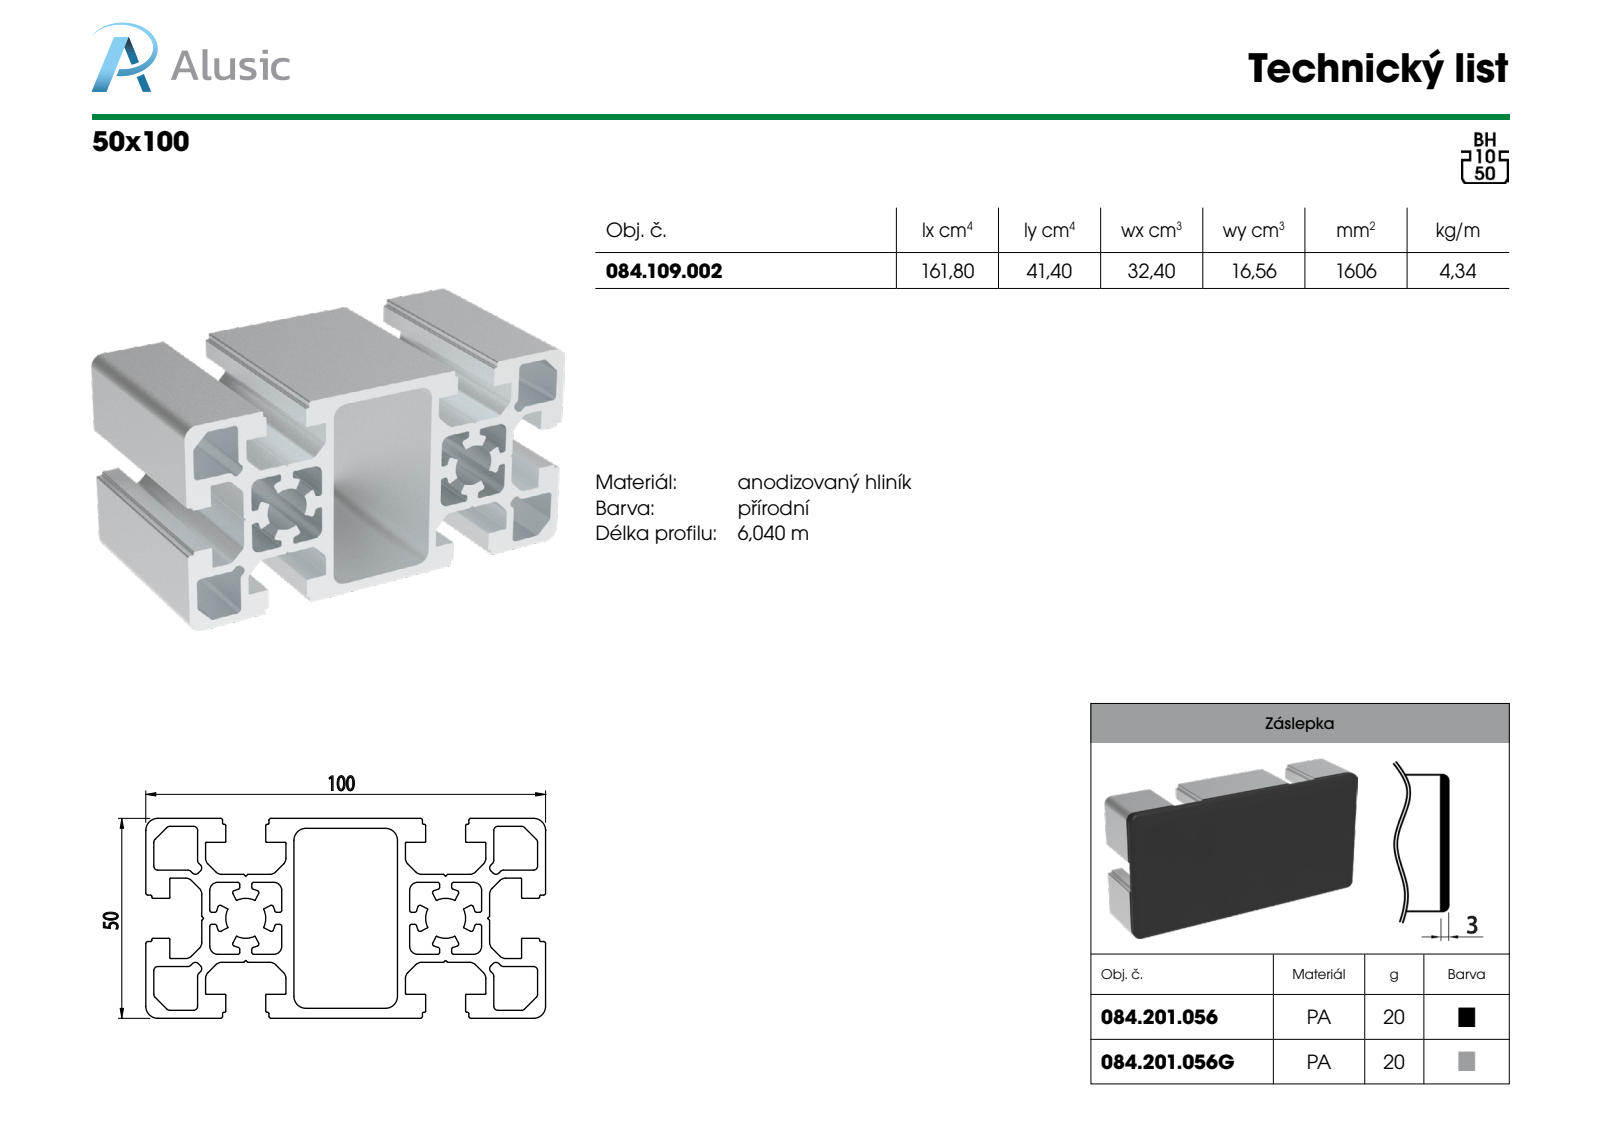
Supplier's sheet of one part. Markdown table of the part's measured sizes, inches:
| quantity | value |
| --- | --- |
| part name | 084.109.002 |
| STEP written by | SolidWorks 2018 (AUTOMOTIVE_DESIGN) |
| units | inches |
| bodies | 1 solid, 443 faces (192 planar, 251 cylindrical, 0 other) |
| overall size | 3.937 × 3.937 × 1.969 |
| volume | 9.802 in³ |
| surface area | 176 in² |
| partial cylindrical surfaces (radius × count) | 0.02 × 60, 0.004 × 34, 0.039 × 32, 0.079 × 32, 0.008 × 24, 0.012 × 24, 0.118 × 8, 0.197 × 2 |
| main face-to-face distances | 0.551, 1.969, 0.079, 1.459, 0.63, 0.787, 0.157, 0.236, 1.102, 0.829 |
